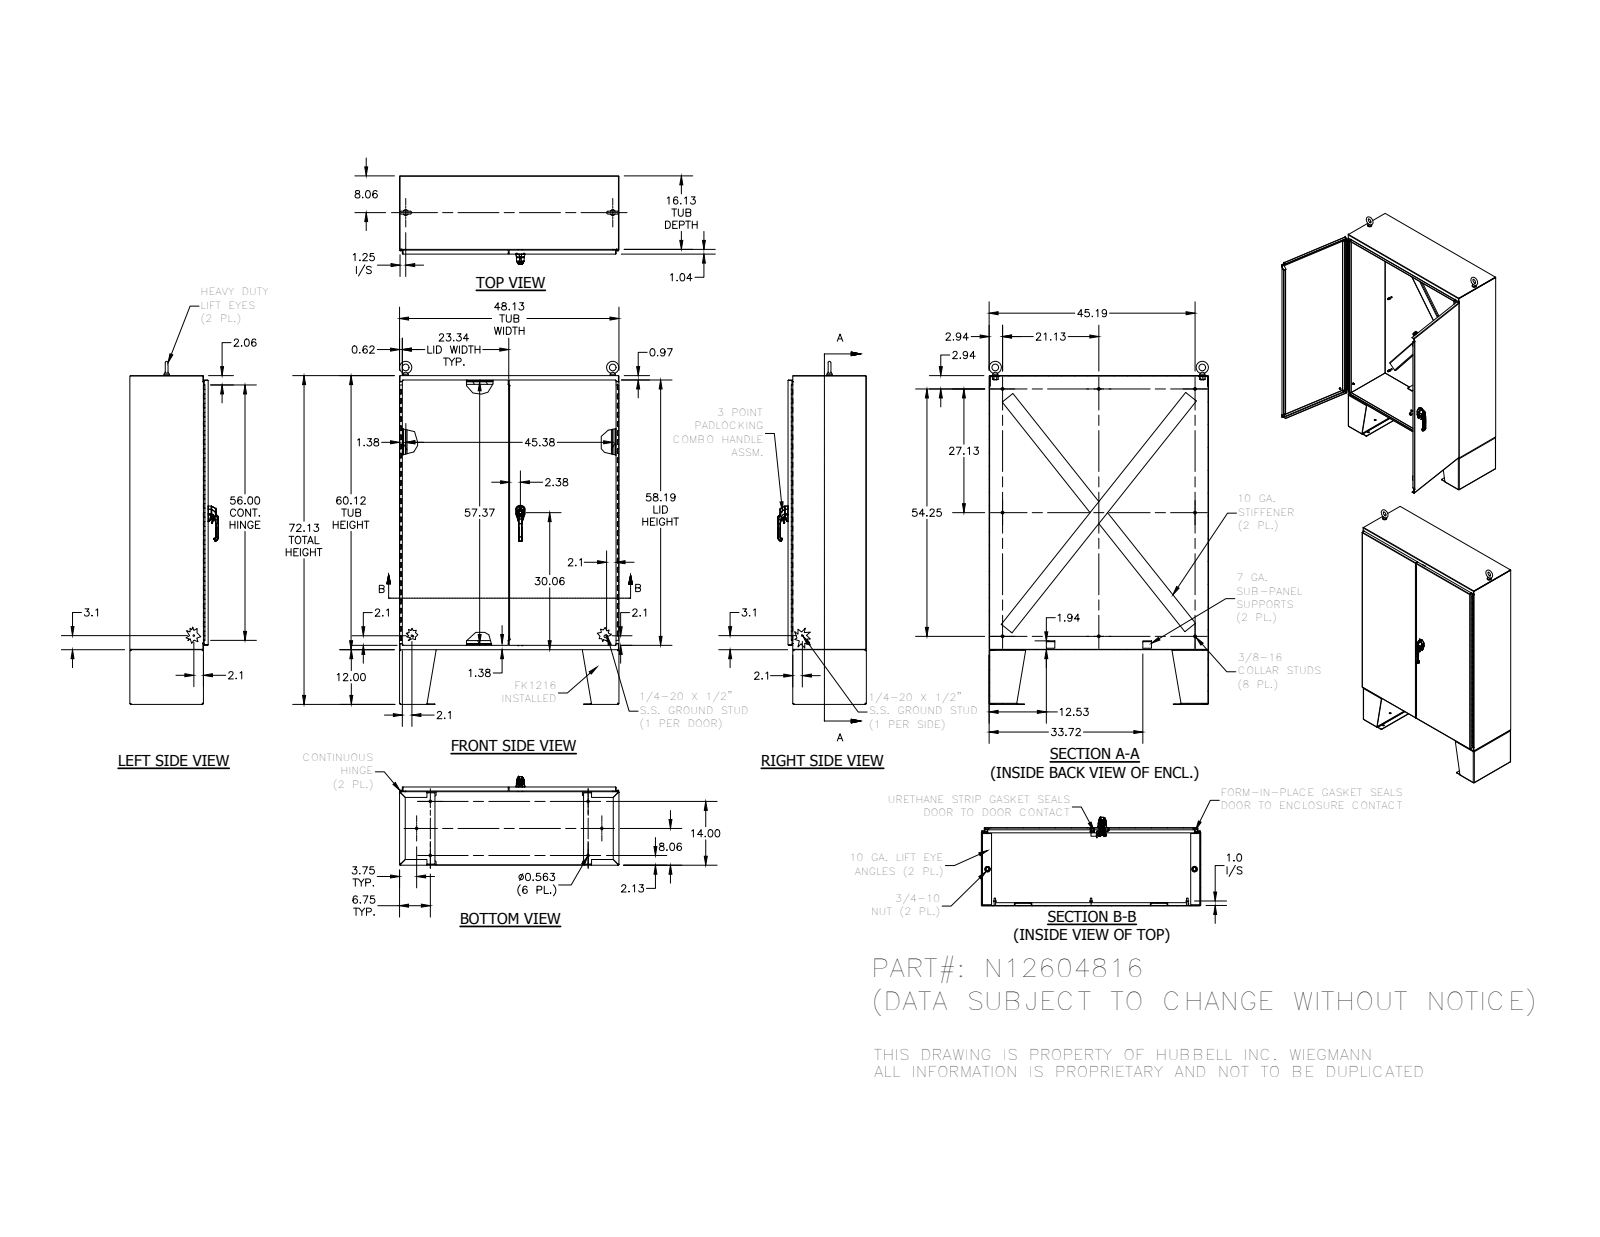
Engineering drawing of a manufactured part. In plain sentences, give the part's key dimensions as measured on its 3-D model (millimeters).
The part is named "N12604816". Its 3-D file was written by "SolidWorks 2018 (AUTOMOTIVE_DESIGN)". It is 76 solids with 2392 faces: 1384 planar, 708 cylindrical and 300 other. Overall it measures 1911.3 by 1222.4 by 491.2 millimeters. Its volume is 20 320 000 cubic millimeters and its surface area 15 960 000 square millimeters. Round holes: 18 of diameter 14.3, 8 of diameter 7, 4 of diameter 5.1, 3 of diameter 7.1, 2 of diameter 3.2, 2 of diameter 3.2, 2 of diameter 6.1, 2 of diameter 6.4, 2 of diameter 6.4, 2 of diameter 10.2, 2 of diameter 11.4, 2 of diameter 16.3. Round bosses or shafts: 8 of diameter 8.4, 5 of diameter 6.4, 4 of diameter 15.9, 4 of diameter 15.9, 3 of diameter 8.6, 2 of diameter 31.8, 2 of diameter 28.4, 2 of diameter 25.4. Partial cylindrical surfaces (rounded edges, fillets, slot ends): 24 of radius 0.8, 23 of radius 2.4, 22 of radius 5.6, 18 of radius 1.3, 16 of radius 0.6, 15 of radius 3.2, 13 of radius 0.8, 8 of radius 1.7. The main face-to-face distances are 2.4, 433.5, 431.1, 435.9, 1220, 1524.8, 1222.4, 1217.6, 3.2, 1522.4. The hole center spacings are 127, 148.6, 166.9, 169, 204, 374.7, 395.6, 873.9.
